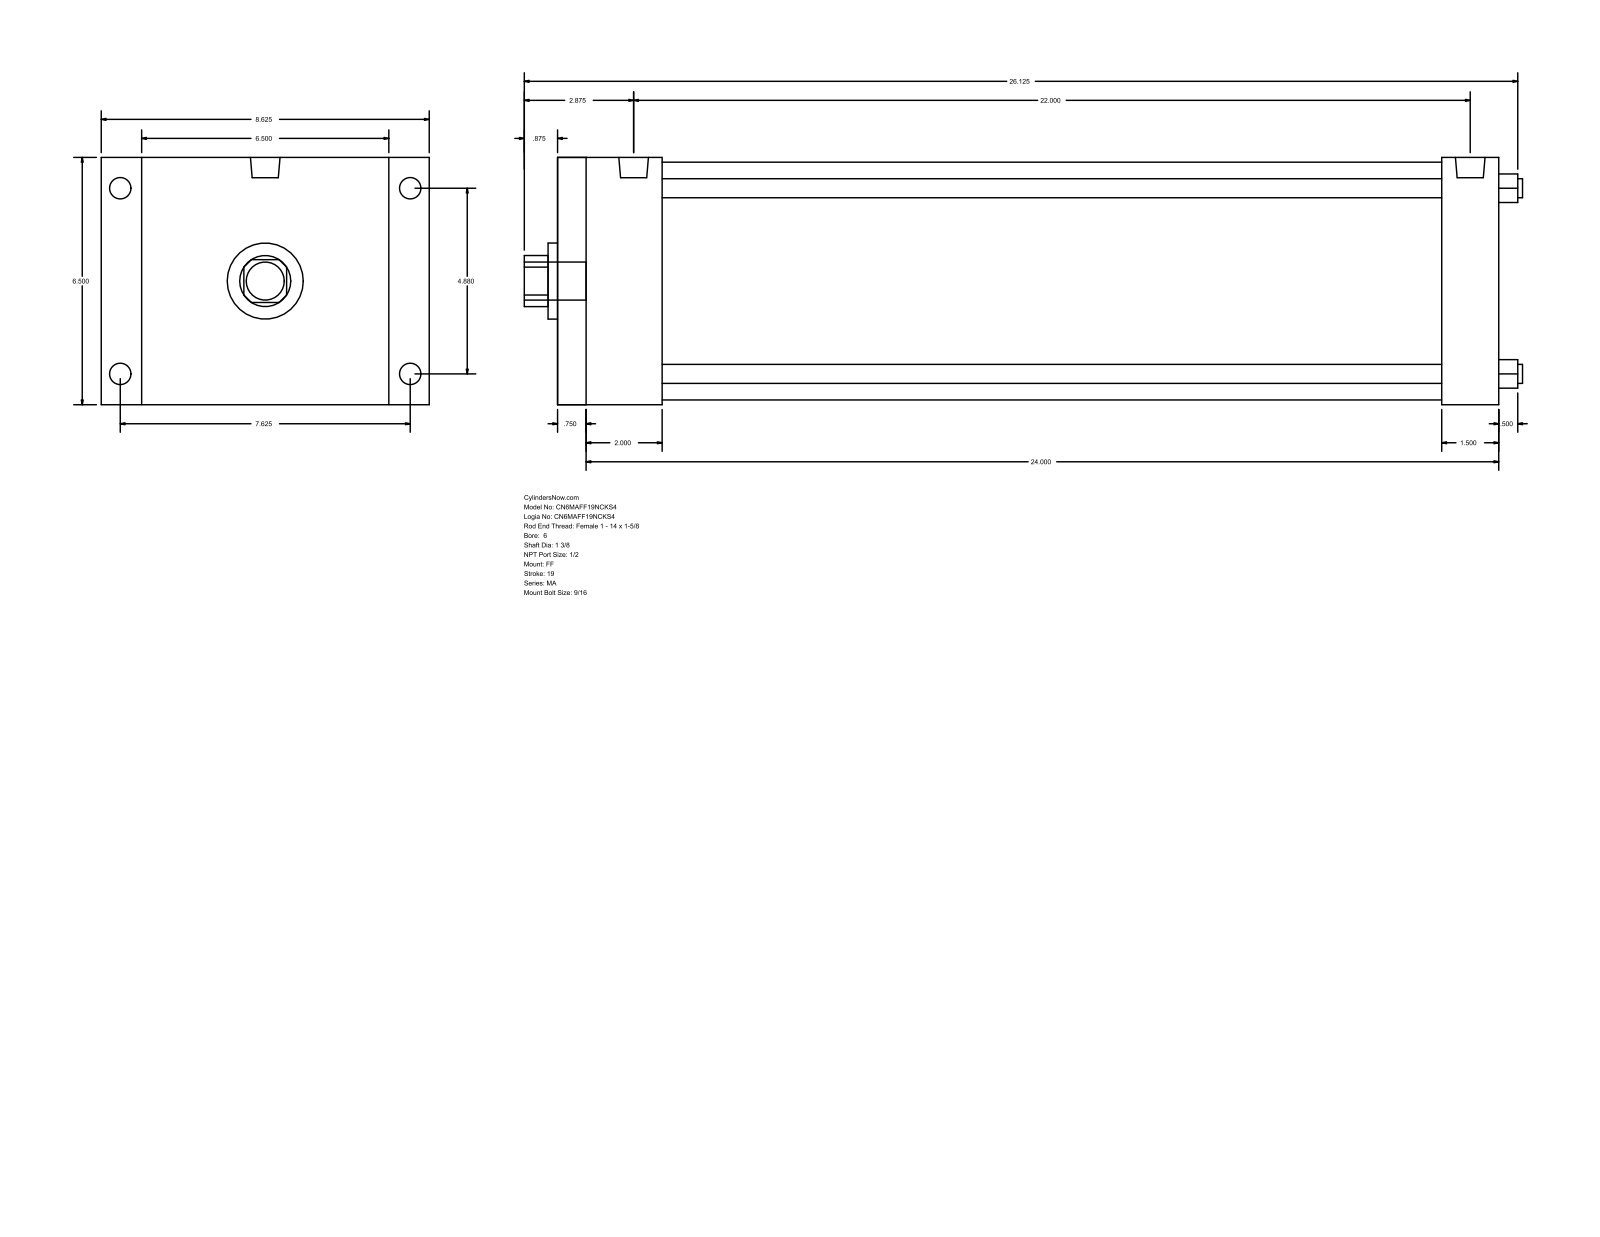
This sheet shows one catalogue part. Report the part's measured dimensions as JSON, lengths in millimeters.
{"part_name": "MA_FF__0600_1.375", "step_written_by": "GSSL Pune (CONFIG_CONTROL_DESIGN)", "units": "millimeters", "bodies": {"solids": 0, "faces": 92, "planar": 64, "cylindrical": 28, "other": 0}, "overall_size": [666.75, 219.07, 165.1], "round_holes": [[12.7, 4], [34.92, 1], [50.8, 1], [158.75, 1]], "round_bosses_or_shafts": [[17.46, 4], [14.29, 4], [19.77, 2], [25.4, 1]], "partial_cylinders_radius": [[17.06, 1]], "face_to_face_distances": [165.1, 628.65, 15.87, 612.78, 66.67, 50.8, 561.98, 590.54, 574.67, 523.87], "hole_center_spacings": [87.65, 123.96, 175.31]}
